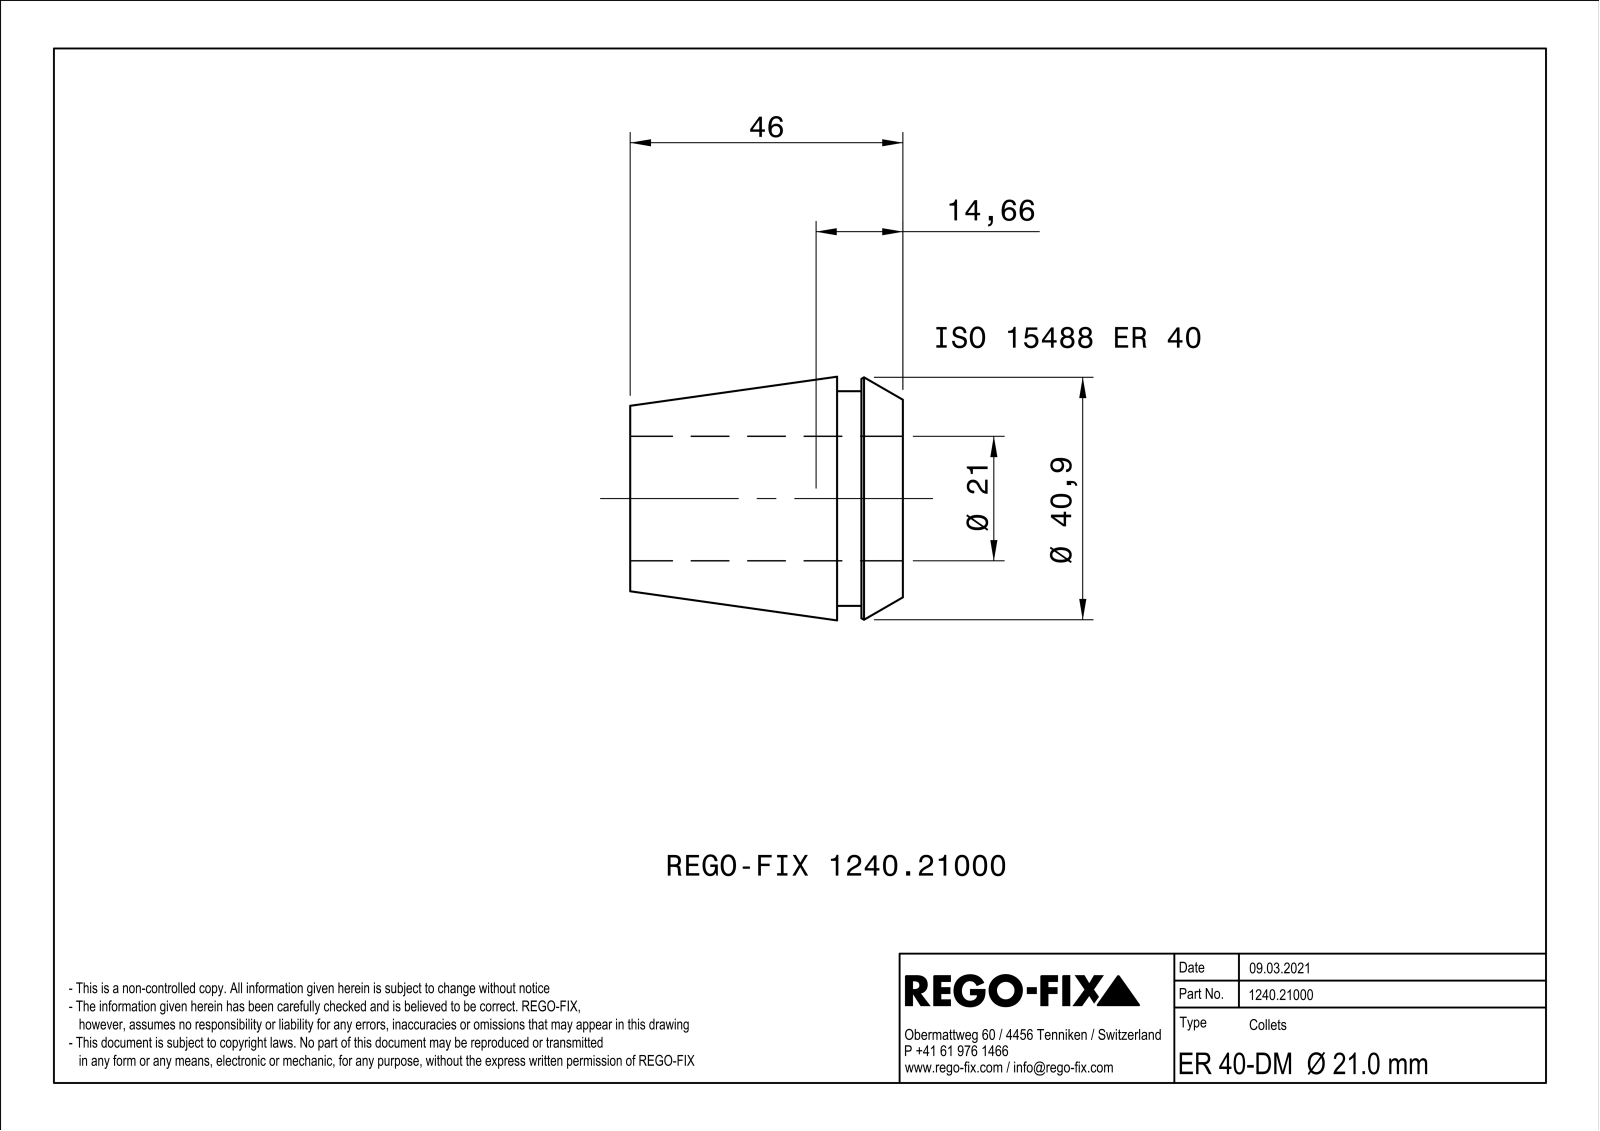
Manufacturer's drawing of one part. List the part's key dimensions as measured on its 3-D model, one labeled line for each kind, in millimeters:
Part name (STEP PRODUCT): NOCUT
STEP written by: SIEMENS PLM Software Solid Edge ST10 (AUTOMOTIVE_DESIGN)
Units: millimetres
Bodies: 1 solid, 154 faces (80 planar, 9 cylindrical, 65 other)
Overall size (bounding box): 46 × 40.99 × 40.99
Volume: 27 653 mm³ · Surface area: 17 253 mm²
Round holes (diameter × count): ⌀21 ×1
Round bosses / shafts (diameter × count): ⌀36.2 ×1
Main face-to-face distances: 1, 46, 11.1, 34.9, 7, 4.1, 39, 17, 10, 5.9
